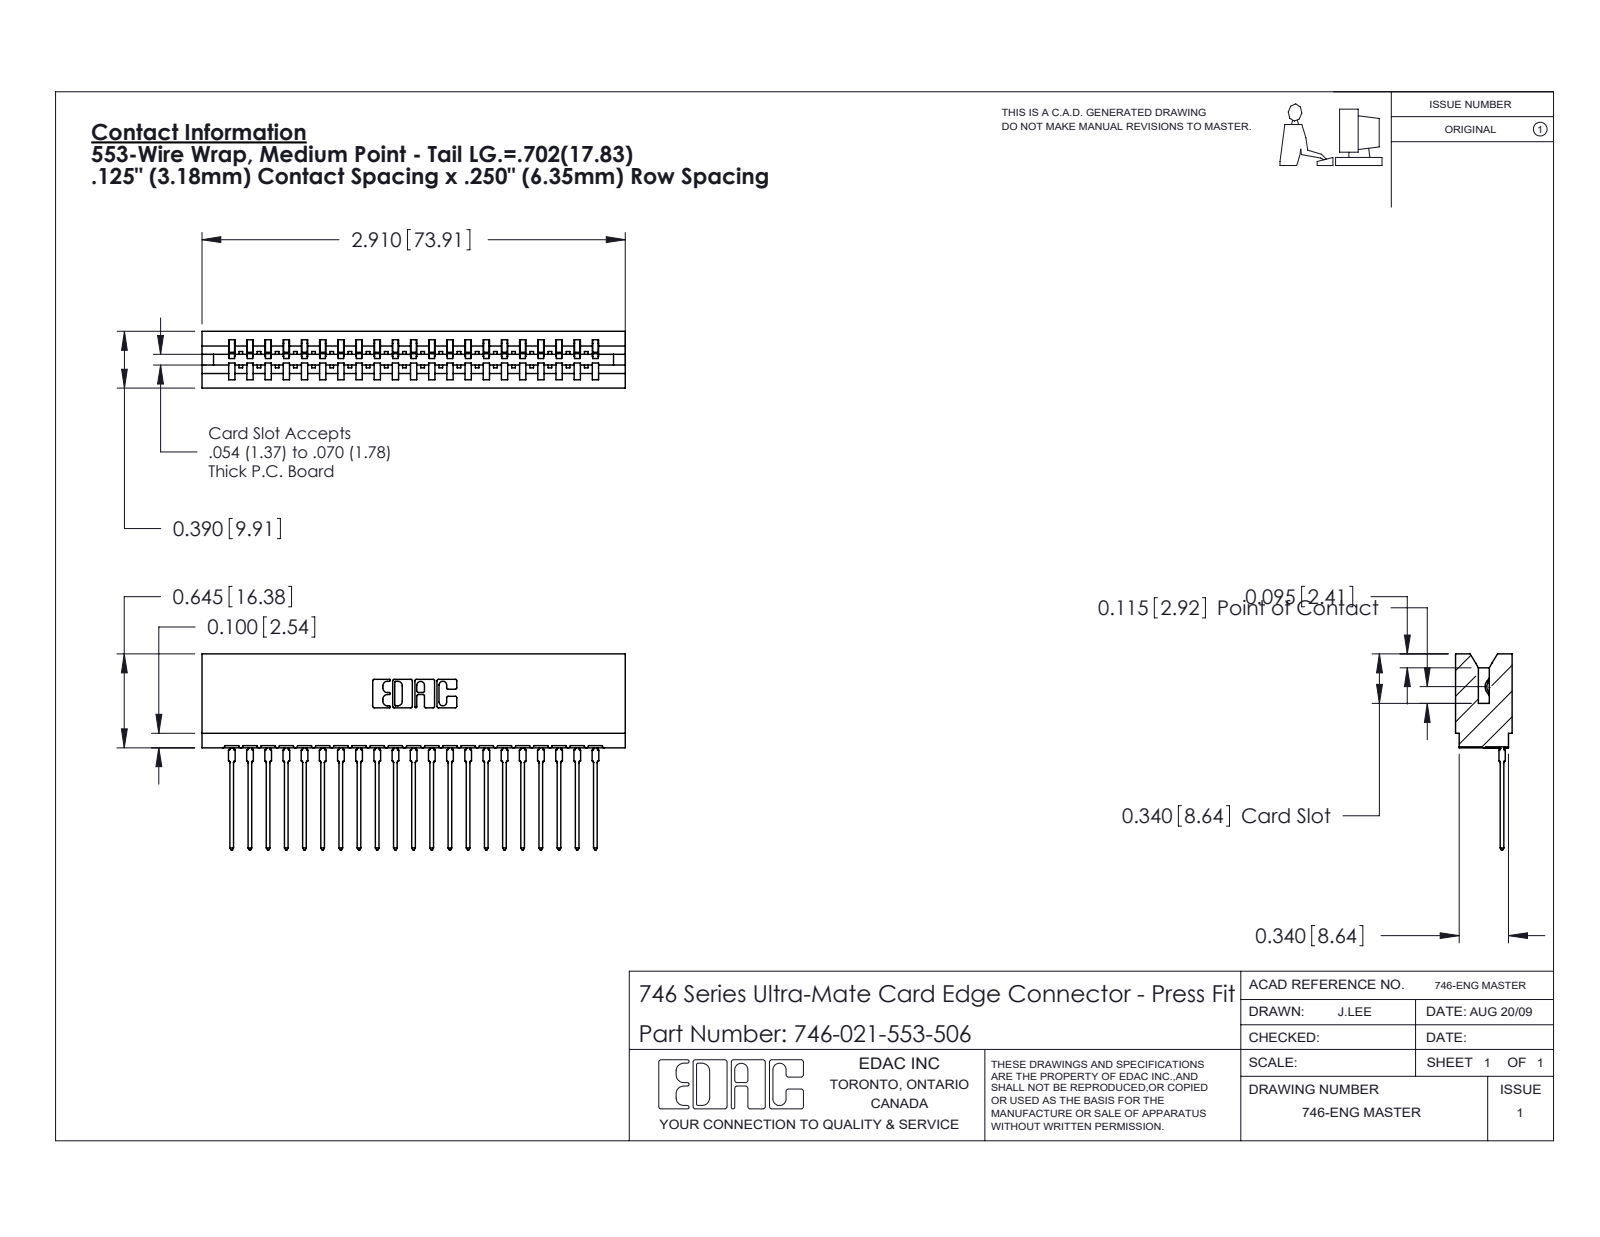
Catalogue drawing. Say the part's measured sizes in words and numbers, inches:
The part is named "746 Part_.340 Slot Depth - 06; 746-292-001_553; 746-021-553-506". Its 3-D file was written by "SolidWorks 2020 (CONFIG_CONTROL_DESIGN)". It is 22 solids with 2366 faces: 1379 planar, 441 cylindrical and 546 other. Overall it measures 2.91 by 1.346 by 0.39 inches. Its volume is 0.518 cubic inches and its surface area 17.87 square inches. Partial cylindrical surfaces (rounded edges, fillets, slot ends): 42 of radius 0.021, 22 of radius 0.01, 22 of radius 0.015, 6 of radius 0.007, 6 of radius 0.031, 4 of radius 0.005, 4 of radius 0.011, 3 of radius 0.026. The main face-to-face distances are 0.333, 0.25, 0.057, 0.39, 0.5, 0.025, 0.307, 0.083, 0.042, 0.125.
